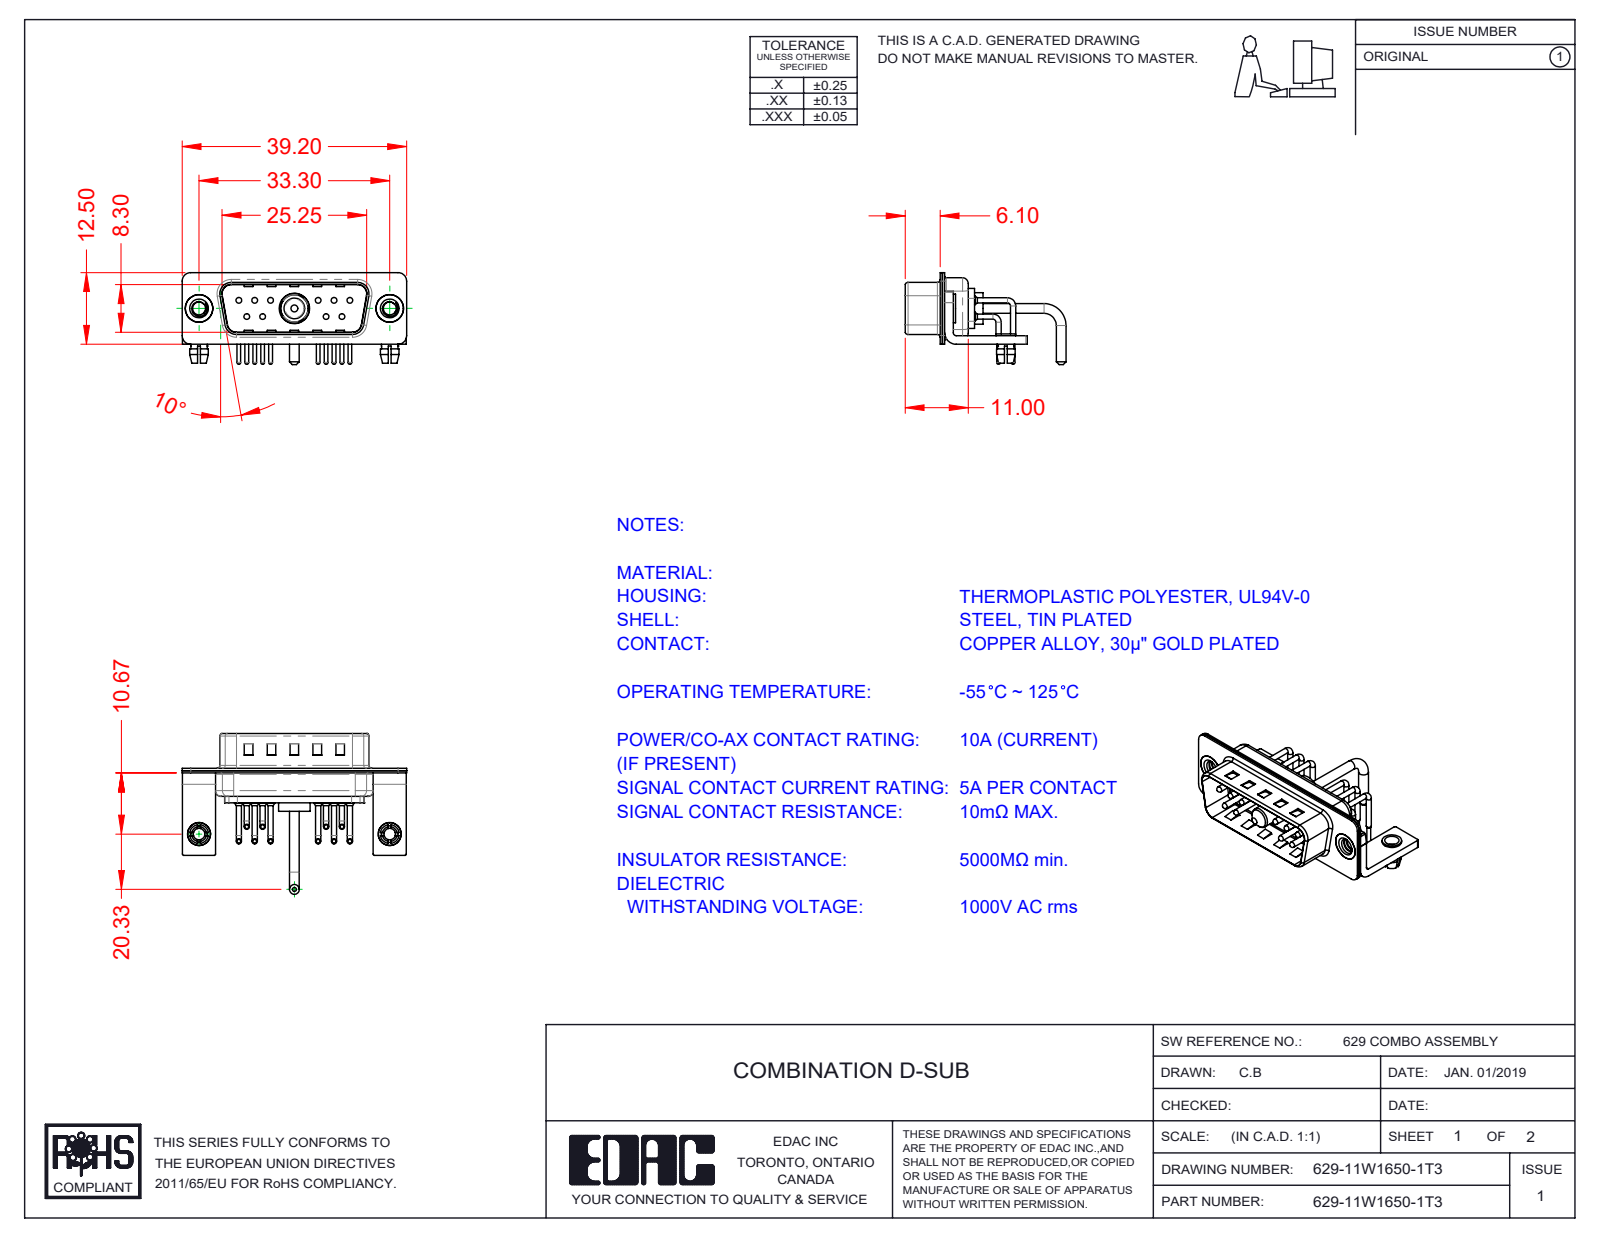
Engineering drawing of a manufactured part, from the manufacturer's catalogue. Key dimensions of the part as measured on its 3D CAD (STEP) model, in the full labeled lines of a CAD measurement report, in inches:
Part name (STEP PRODUCT): 629Combo Threaded Rivet_3; 629Combo Stabilizer Bracket; 629Combo Contact Row 1; 629Combo Board Lock (+6 more)
STEP written by: SolidWorks 2020 (CONFIG_CONTROL_DESIGN)
Units: inches
Bodies: 21 solids, 1628 faces (866 planar, 568 cylindrical, 194 other)
Overall size (bounding box): 1.543 × 1.106 × 0.632
Volume: 0.142 in³ · Surface area: 9.328 in²
Round holes (diameter × count): ⌀0.079 ×12, ⌀0.03 ×10, ⌀0.063 ×10, ⌀0.089 ×2, ⌀0.098 ×2, ⌀0.126 ×2, ⌀0.157 ×2, ⌀0.189 ×2, ⌀0.191 ×1, ⌀0.209 ×1
Round bosses / shafts (diameter × count): ⌀0.035 ×20, ⌀0.059 ×10, ⌀0.039 ×10, ⌀0.026 ×10, ⌀0.197 ×2, ⌀0.193 ×2, ⌀0.157 ×2, ⌀0.134 ×2
Partial cylindrical surfaces — rounded edges, fillets, slot ends (radius × count): R0.01 ×16, R0.059 ×16, R0.079 ×13, R0.04 ×10, R0.02 ×9, R0.063 ×8, R0.039 ×7, R0.024 ×4
Main face-to-face distances: 0.016, 0.031, 0.059, 0.374, 0.358, 0.343, 0.39, 0.024, 0.075, 0.205
Hole centre spacings: 0.124, 0.109, 0.545, 0.436, 0.654, 0.198, 0.198, 0.218
